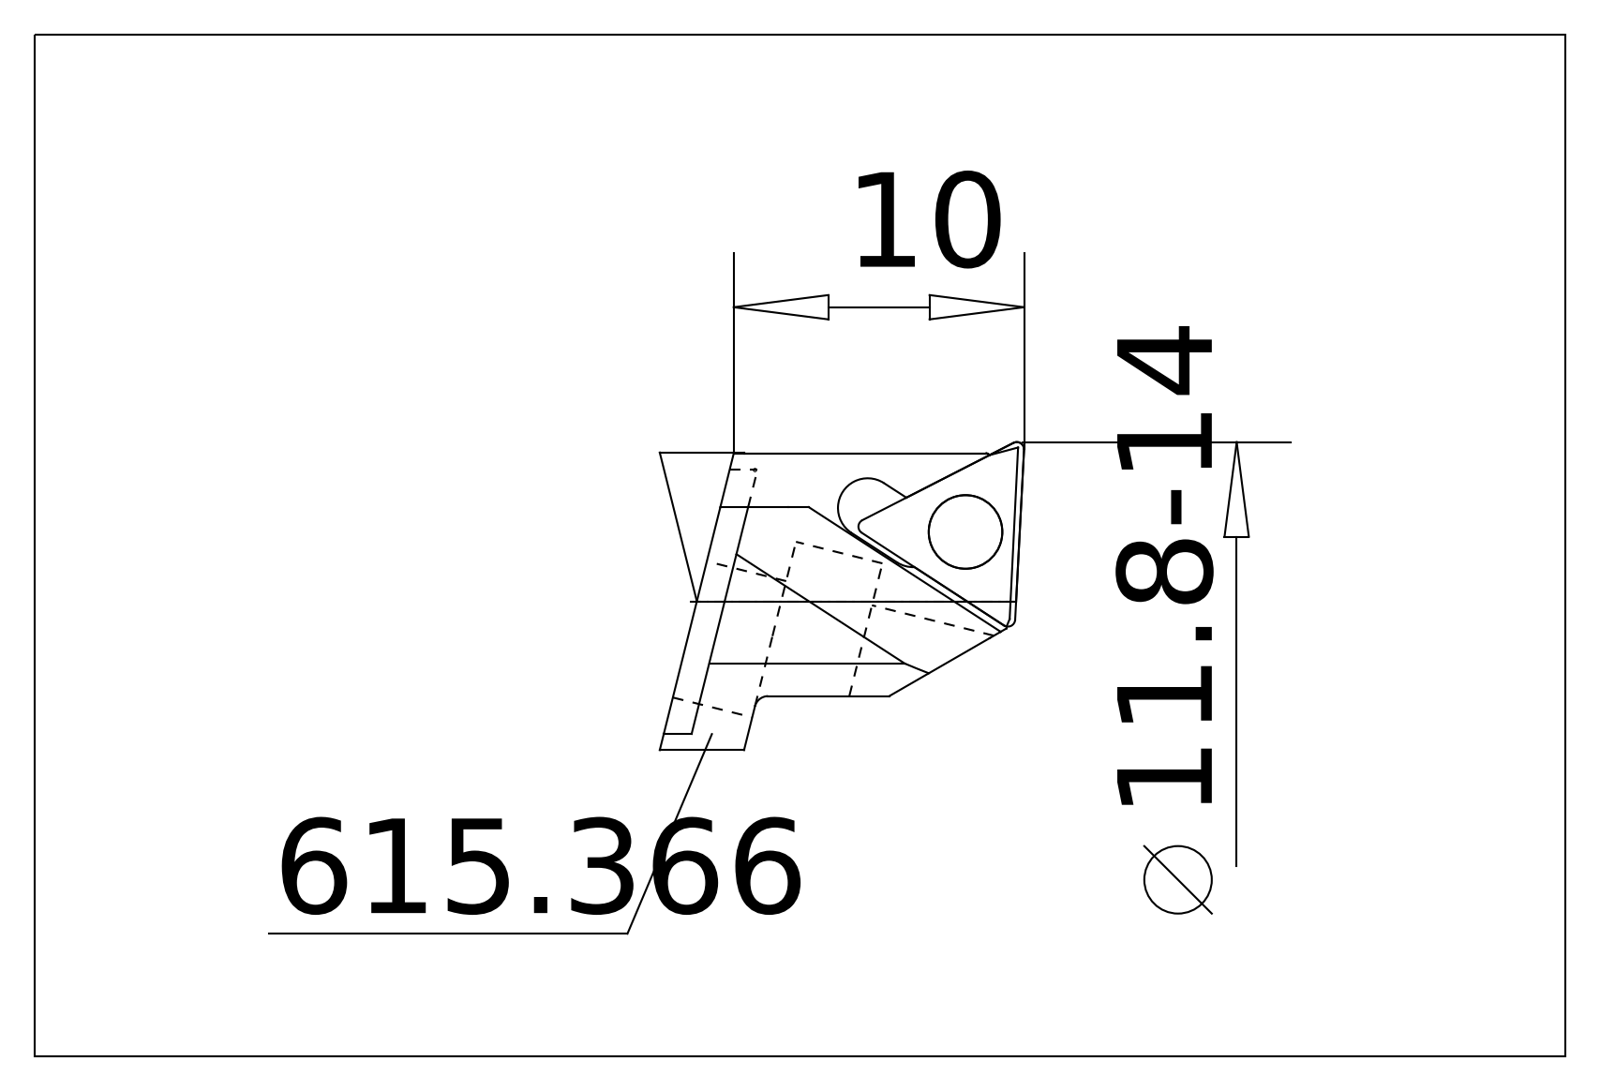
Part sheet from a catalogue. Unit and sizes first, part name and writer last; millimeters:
Units: millimetres
Overall size (bounding box): 14.52 × 11.41 × 10
Round holes (diameter × count): ⌀2.3 ×2, ⌀1.56 ×1
Round bosses / shafts (diameter × count): ⌀2.7 ×1, ⌀2 ×1
Partial cylindrical surfaces — rounded edges, fillets, slot ends (radius × count): R0.15 ×6, R0.3 ×6, R1.1 ×2, R2.1 ×2, R3.6 ×2, R0.5 ×1, R2.25 ×1, R5.5 ×1
Main face-to-face distances: 2.5, 5, 1, 4, 3, 10, 7.5, 2.45, 1.4, 8.6
Volume: 579 mm³ · Surface area: 987 mm²
Bodies: 5 solids, 152 faces (52 planar, 50 cylindrical, 50 other)
Part name (STEP PRODUCT): 615.366 Kaiser E12_14 TP07|651.735 Kaiser TPGT 070203 K10C;Kombinieren1; 615.366 Kaiser E12_14 TP07|694.103 Kaiser ETL M2x4.8 T6 IP 10S;Kreismuster1; 615.366 Kaiser E12_14 TP07|615.366 Kaiser E12_14 TP07-2;Verrundung1; 615.366 Kaiser E12_14 TP07|615.366 Kaiser E12_14 TP07-1;<N017.30 (TP 0702) PLS links Freistellung links>-<<0640.020>-<Schnitt-Linear austragen1>> (+1 more)
STEP written by: ACIS (automotive_design)
